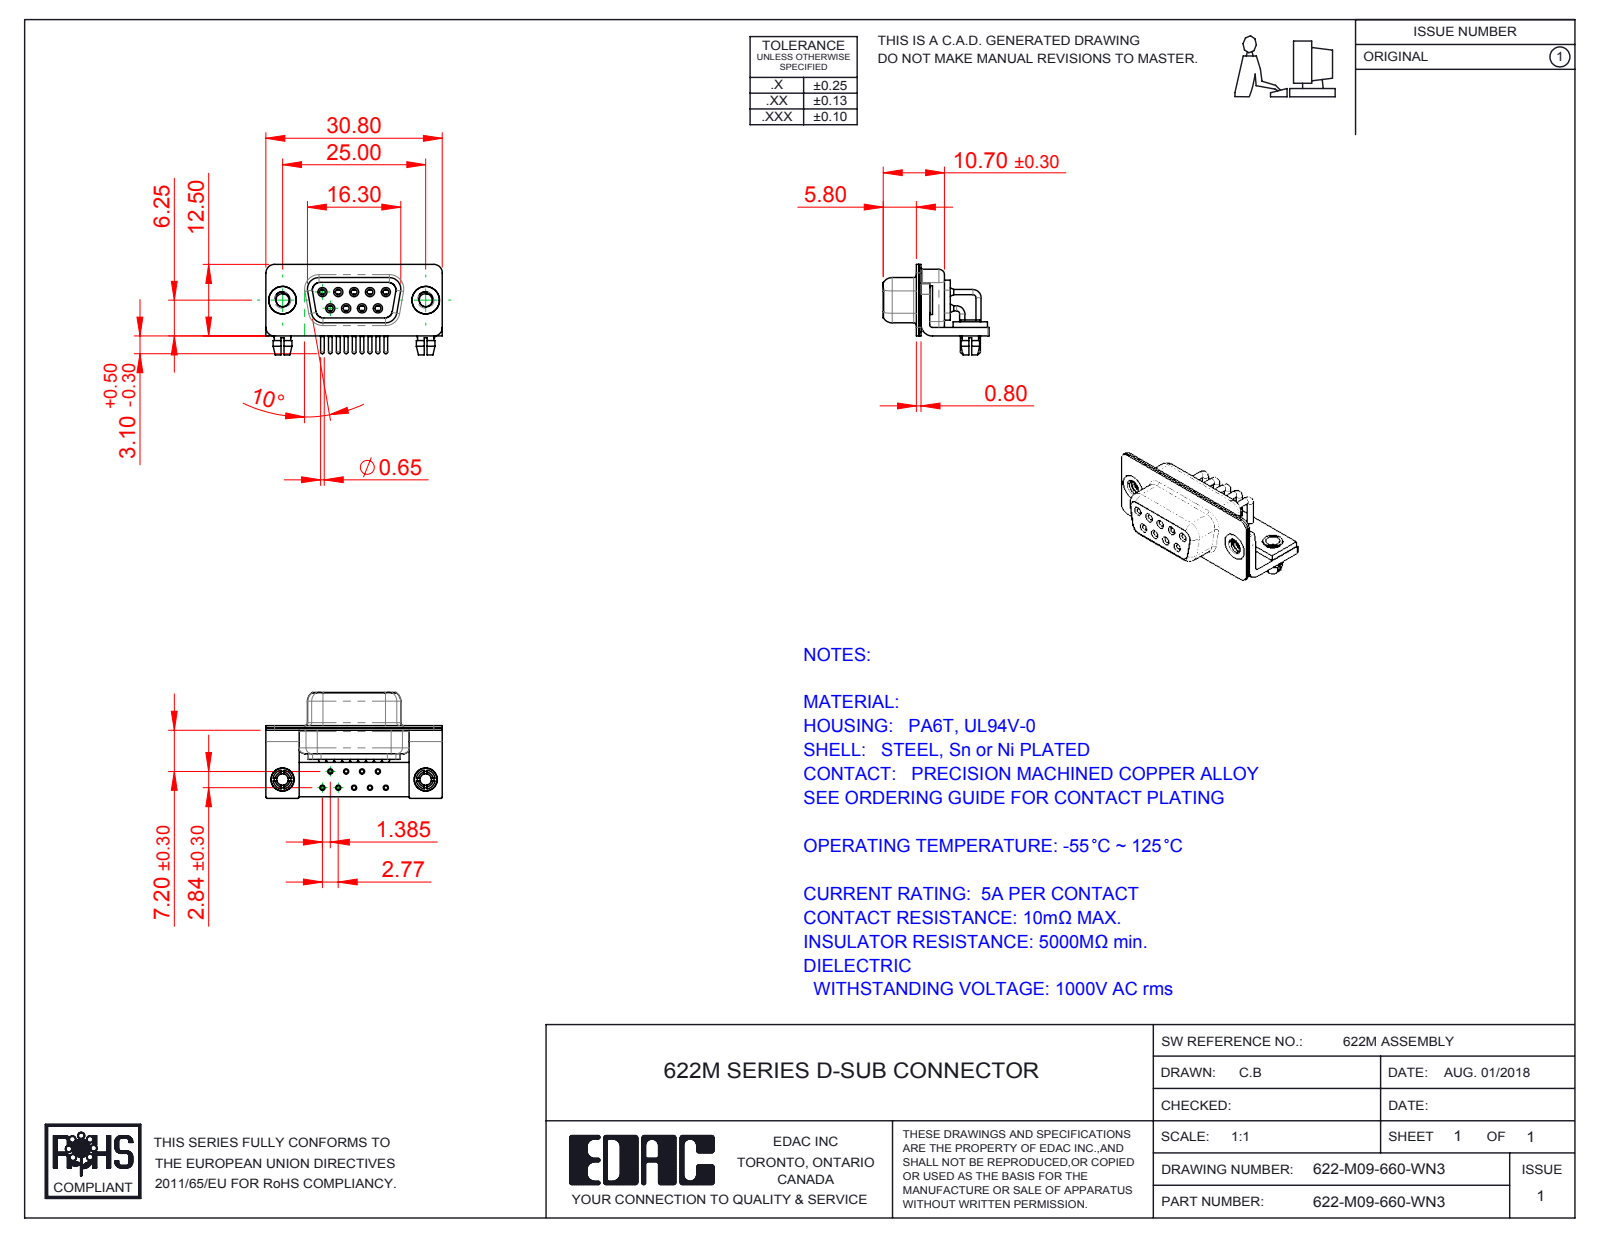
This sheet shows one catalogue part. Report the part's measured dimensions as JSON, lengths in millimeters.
{"part_name": "622M Contact Row 2; 622M Contact Row 1; 622M Shell Rear_09 Contacts; 622M Shell Front_09 Contacts (+6 more)", "step_written_by": "SolidWorks 2016 (CONFIG_CONTROL_DESIGN)", "units": "millimeters", "bodies": {"solids": 19, "faces": 916, "planar": 276, "cylindrical": 416, "other": 224}, "overall_size": [30.8, 18.5, 15.8], "volume_mm3": 2177, "surface_area_mm2": 5763, "round_holes": [[2, 11], [0.9, 9], [1, 9], [1.1, 9], [1.7, 9], [1.8, 9], [2.26, 2], [2.5, 2], [3.2, 2], [4, 2], [4.8, 2]], "round_bosses_or_shafts": [[1.6, 9], [1.5, 9], [0.9, 9], [0.65, 9], [5, 2], [4.9, 2], [4, 2], [3.4, 2]], "partial_cylinders_radius": [[0.25, 16], [1.5, 16], [2, 13], [1.35, 8], [1.6, 8], [0.5, 5], [0.6, 4], [0.65, 4]], "face_to_face_distances": [0.4, 0.8, 1.5, 2.3, 1.9, 1, 9.35, 1.45, 8.95, 0.85], "hole_center_spacings": [3.16, 2.77, 5.54, 5.03, 5.04, 8.31, 7.48, 7.49]}
